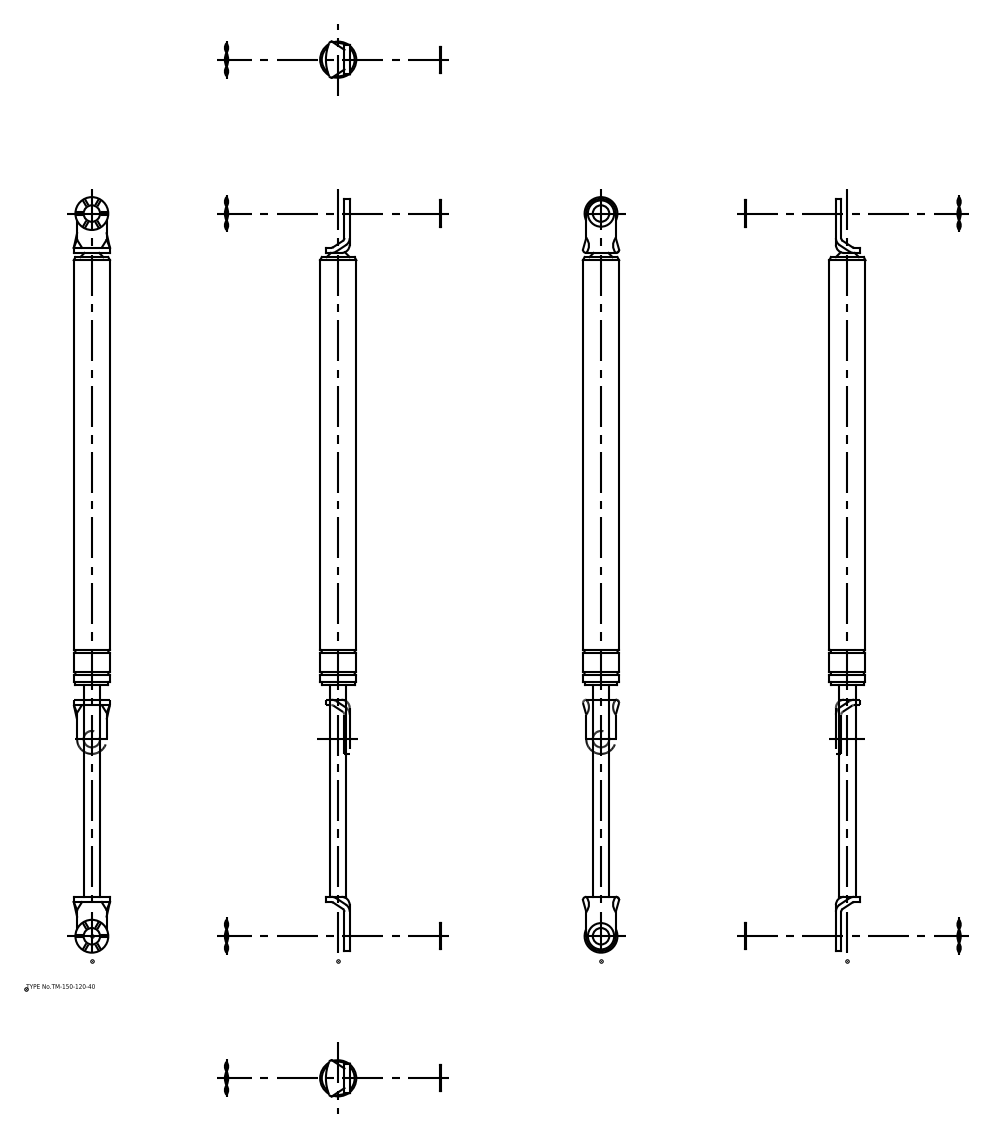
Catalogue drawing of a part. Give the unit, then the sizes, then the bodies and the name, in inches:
Units: inches
Overall size (bounding box): 18.11 × 0.886 × 0.886
Round holes (diameter × count): ⌀0.394 ×2
Round bosses / shafts (diameter × count): ⌀0.787 ×3, ⌀0.63 ×2, ⌀0.886 ×1, ⌀0.866 ×1, ⌀0.394 ×1
Partial cylindrical surfaces — rounded edges, fillets, slot ends (radius × count): R0.173 ×2, R0.197 ×2, R0.354 ×2, R1.036 ×1
Main face-to-face distances: 0.126, 0.079, 0.205, 15.559, 0.224, 0.146, 0.02, 10.48, 5.205, 15.685
Hole centre spacings: 17.323
Volume: 7.014 in³ · Surface area: 44.26 in²
Bodies: 6 solids, 94 faces (42 planar, 44 cylindrical, 8 other)
Part name (STEP PRODUCT): ウェーブワッシャー; ワッシャー; 本体; 本体_div
STEP written by: spGate 16.7.1 (AUTOMOTIVE_DESIGN)
